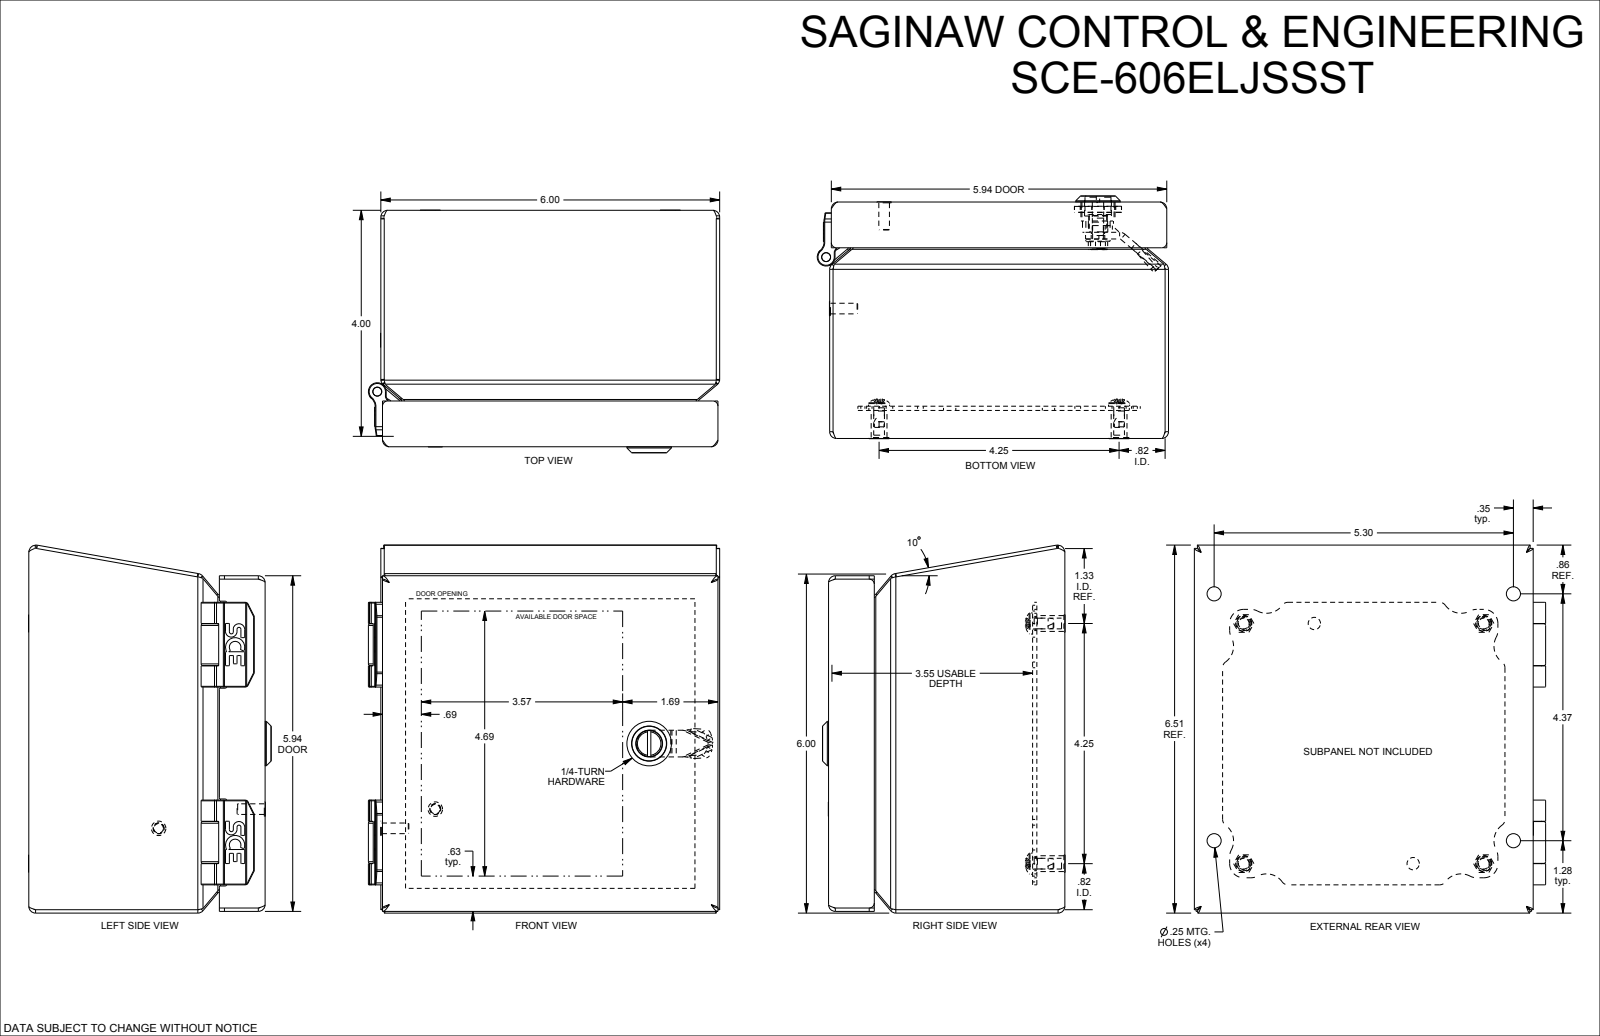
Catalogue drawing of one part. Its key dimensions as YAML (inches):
part_name: "SCE-606ELJSSST"
step_written_by: "SolidWorks 2021 (AUTOMOTIVE_DESIGN)"
units: inches
bodies: {solids: 34, faces: 1454, planar: 566, cylindrical: 353, other: 535}
overall_size: [6.533, 6.22, 4.296]
volume: 15.38
surface_area: 478.3
round_holes:
  - {diameter: 0.16, count: 4}
  - {diameter: 0.19, count: 4}
  - {diameter: 0.25, count: 4}
  - {diameter: 0.284, count: 4}
  - {diameter: 0.02, count: 2}
  - {diameter: 0.1, count: 2}
  - {diameter: 0.218, count: 2}
  - {diameter: 0.266, count: 2}
  - {diameter: 0.158, count: 1}
  - {diameter: 0.196, count: 1}
  - {diameter: 0.2, count: 1}
  - {diameter: 0.239, count: 1}
round_bosses_or_shafts:
  - {diameter: 0.188, count: 6}
  - {diameter: 0.483, count: 4}
  - {diameter: 0.373, count: 4}
  - {diameter: 0.28, count: 4}
  - {diameter: 0.237, count: 4}
  - {diameter: 0.16, count: 4}
  - {diameter: 0.26, count: 2}
  - {diameter: 0.256, count: 2}
partial_cylinders:
  - {radius: 0.03, count: 50}
  - {radius: 0.008, count: 24}
  - {radius: 0.013, count: 21}
  - {radius: 0.25, count: 13}
  - {radius: 0.125, count: 11}
  - {radius: 0.01, count: 10}
  - {radius: 0.06, count: 10}
  - {radius: 0.344, count: 8}
face_to_face_distances: [0.059, 0.06, 5.941, 4.185, 4.126, 4.125, 4.066, 0.571, 0.512, 3.554]
hole_center_spacings: [3.5, 4.25, 0.018, 0.663, 0.763, 1.25, 2.157, 3]
